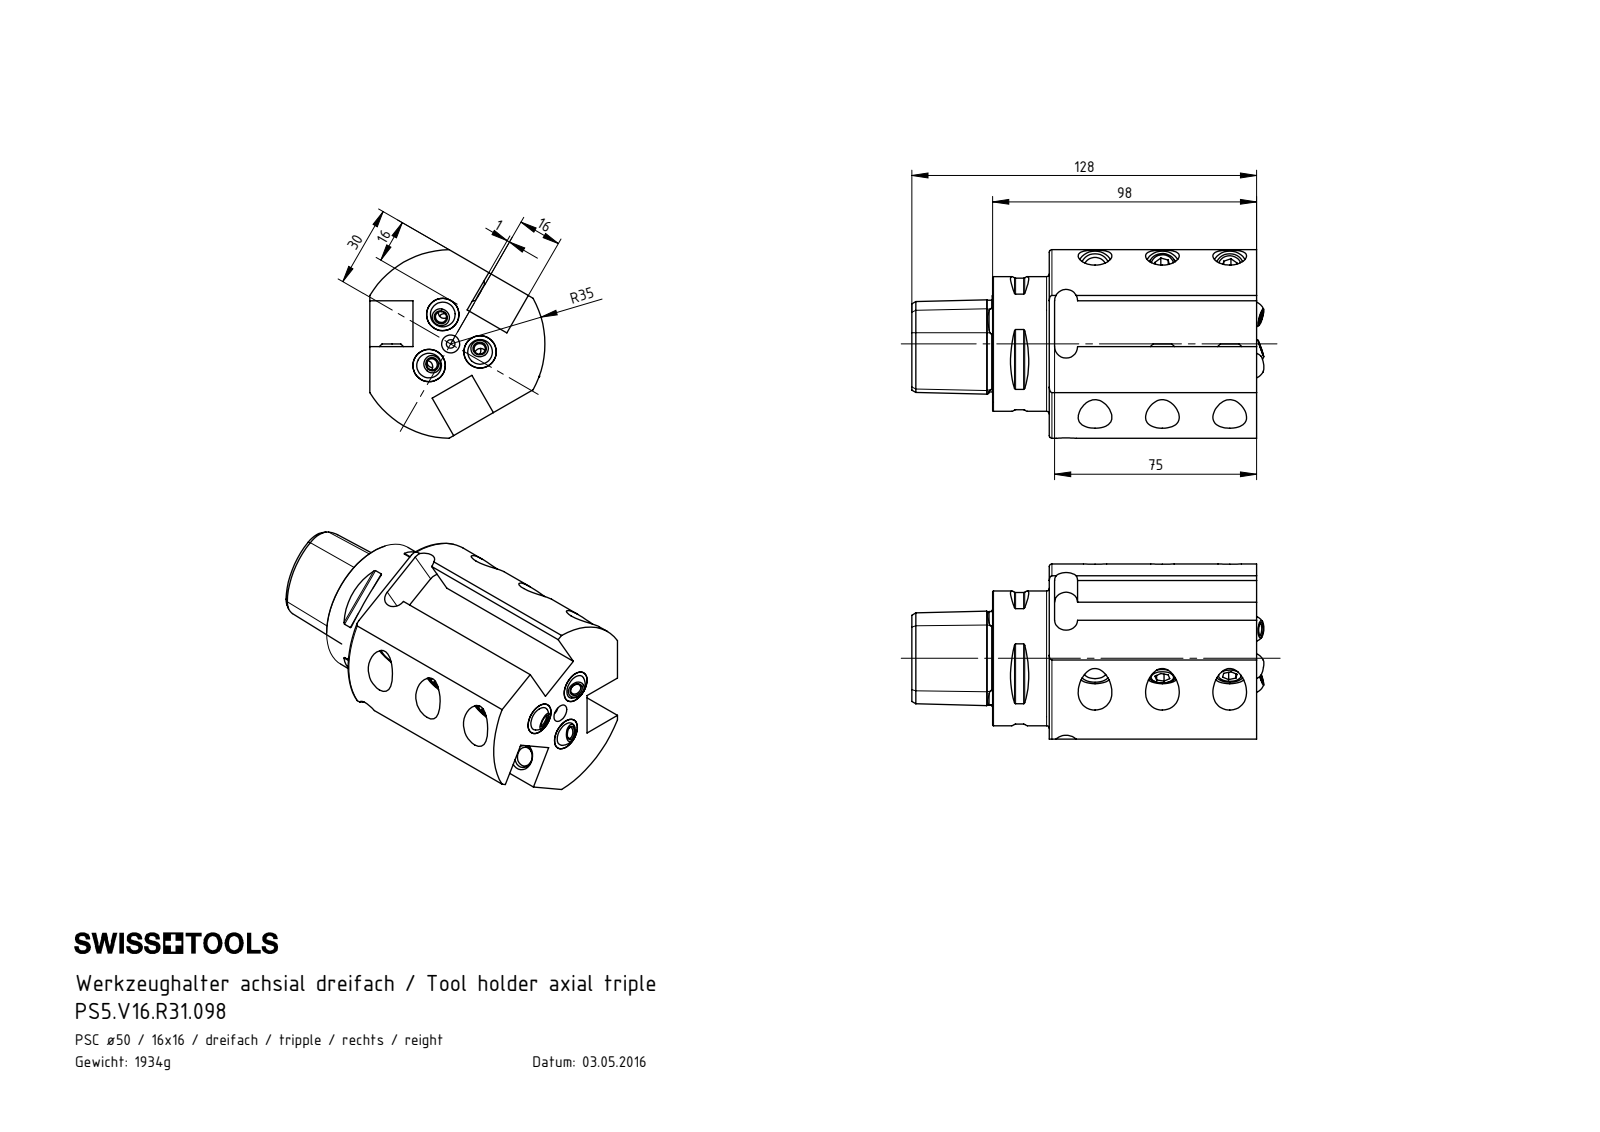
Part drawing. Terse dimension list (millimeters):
name: KU1-U12.001.010_1; ISO 4026 - M10 x 20; KU1-U12.001.010; KU1-U12.001.010_2 (+2 more)
written by: SolidWorks 2017 (AUTOMOTIVE_DESIGN)
unit: mm
bodies: 13 solids, 279 faces (113 planar, 67 cylindrical, 99 other)
size: 129.8 × 69.99 × 65
volume: 246 151 mm³; area: 56 734 mm²
holes: 9× ⌀8.2, 9× ⌀12.5, 6× ⌀4.2, 3× ⌀7, 3× ⌀12, 1× ⌀3.15, 1× ⌀4, 1× ⌀6.1, 1× ⌀8.4, 1× ⌀14.5, 1× ⌀21, 1× ⌀24
bosses: 6× ⌀10, 1× ⌀50
rounds: 8× R0.5, 6× R5, 1× R4, 1× R35
face distances: 16, 17, 77, 2, 75, 21, 23, 98, 90, 69
hole spacings: 25, 19.6, 50, 11.32, 11.31, 26, 34.06, 55.54
